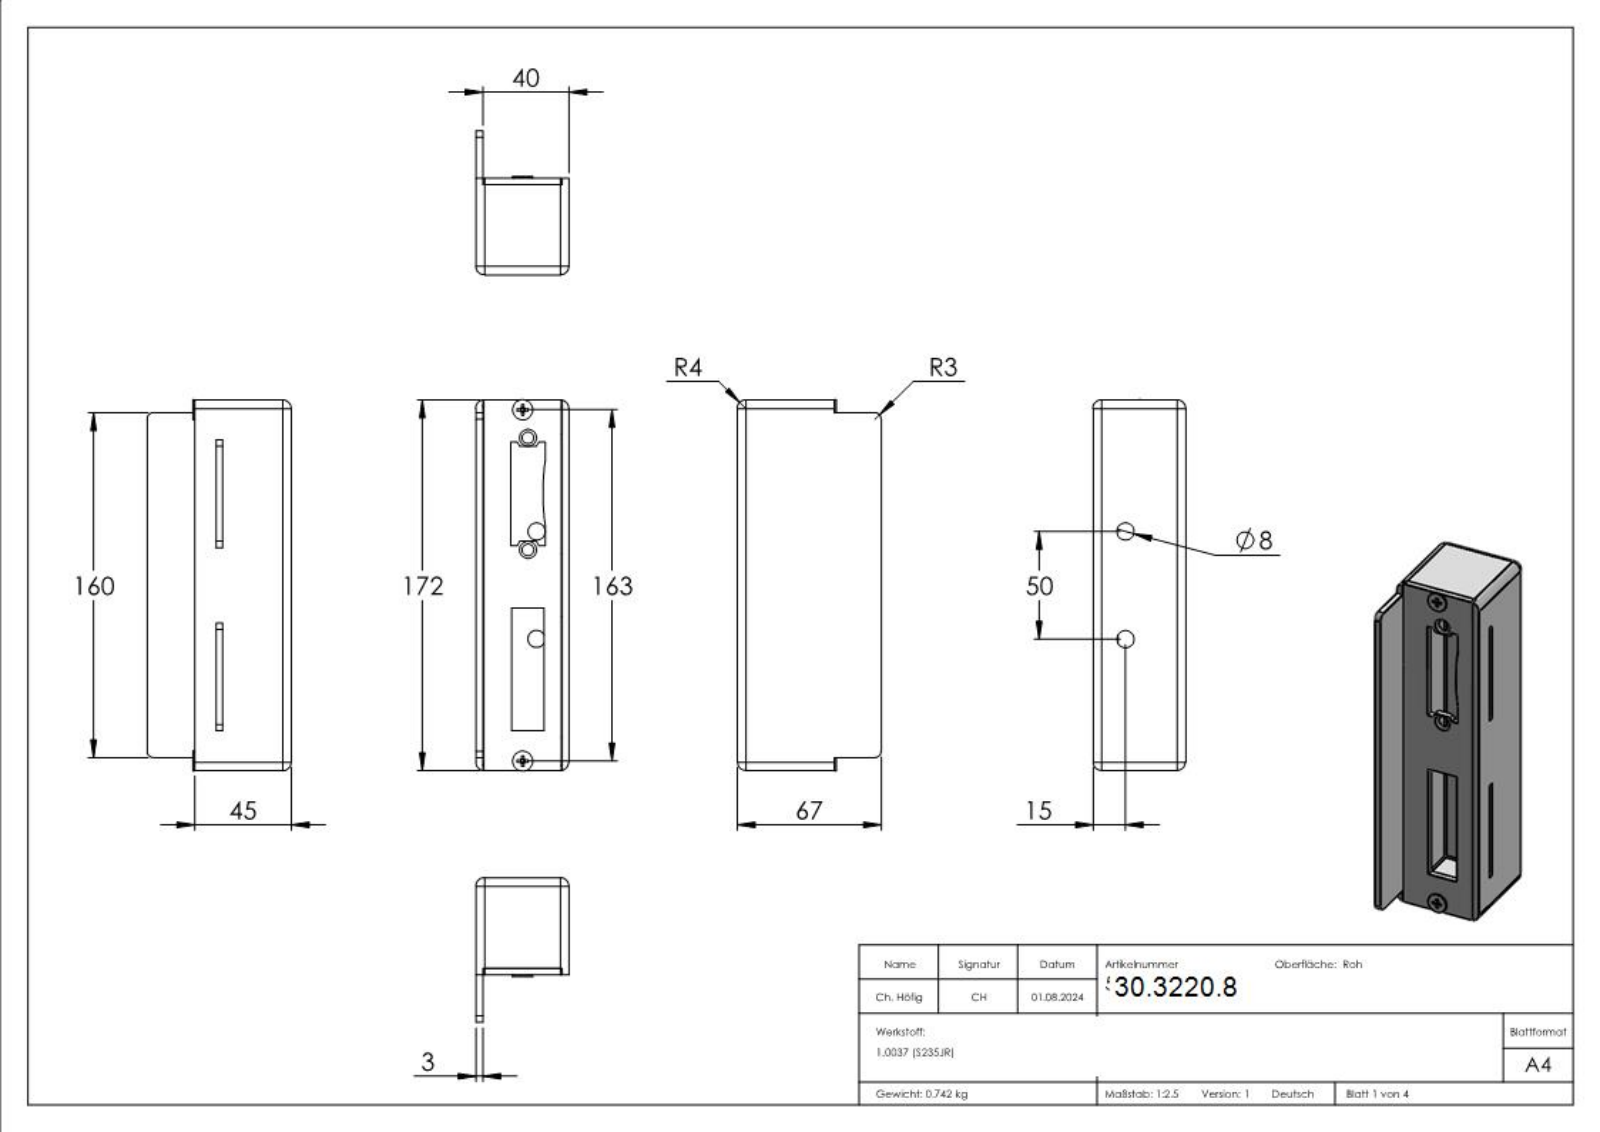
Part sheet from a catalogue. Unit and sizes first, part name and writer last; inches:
Units: inches
Overall size (bounding box): 6.783 × 2.638 × 1.693
Round holes (diameter × count): ⌀0.165 ×2, ⌀0.213 ×2, ⌀0.244 ×2, ⌀0.315 ×2
Round bosses / shafts (diameter × count): ⌀0.366 ×2, ⌀0.197 ×2
Partial cylindrical surfaces — rounded edges, fillets, slot ends (radius × count): R0.039 ×8, R0.157 ×8, R0.02 ×4, R0.118 ×2, R4.449 ×1
Main face-to-face distances: 0.118, 1.575, 1.654, 1.457, 1.693, 1.772, 1.535, 0.075, 6.697, 0.138
Hole centre spacings: 2.239, 4.201, 0.37, 0.521, 1.641, 1.72, 1.969, 2.047
Volume: 5.82 in³ · Surface area: 109.7 in²
Bodies: 4 solids, 234 faces (105 planar, 55 cylindrical, 74 other)
Part name (STEP PRODUCT): countersunk flat head cross recess screw_din_ISO 7046-1 - M5 x 10 - Z --- 10S; 59110-ST; 591xx-ST Teil2_59110-SB; 591xx-ST Teil1_40mm
STEP written by: SolidWorks 2018 (CONFIG_CONTROL_DESIGN)
